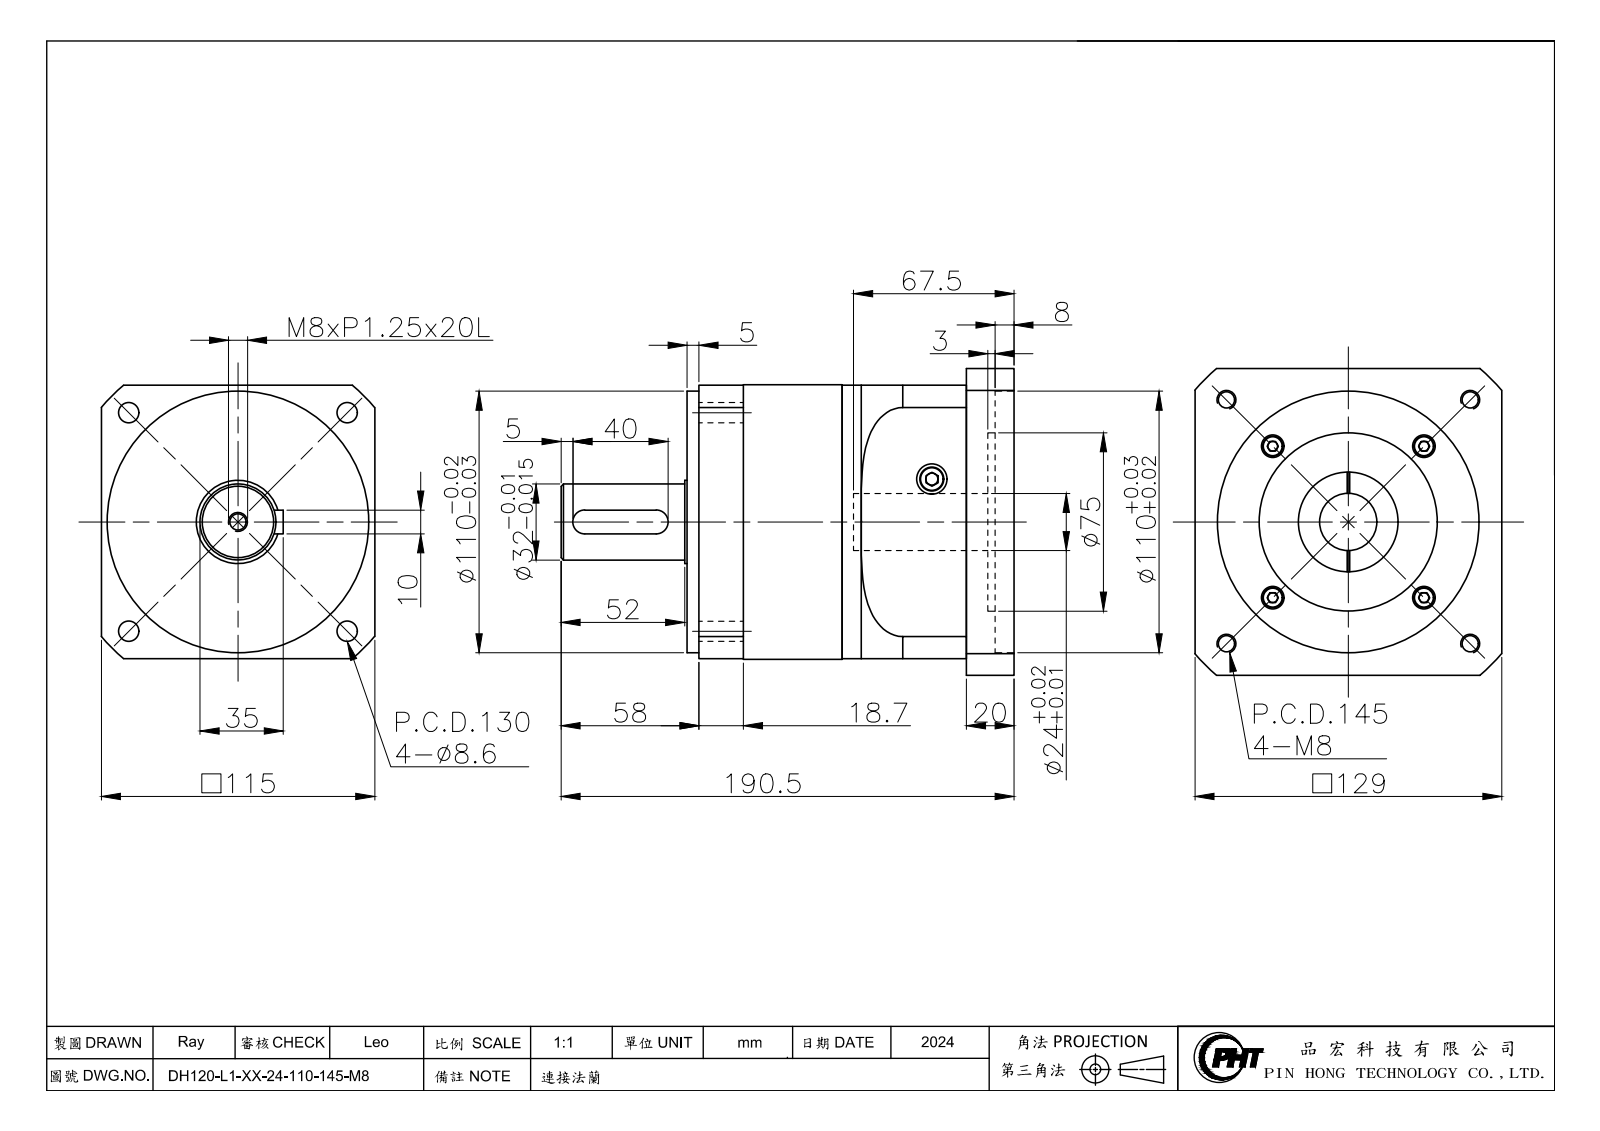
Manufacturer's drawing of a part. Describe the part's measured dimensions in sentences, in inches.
The part is named "DH120-L1-XX-24-110-145-M8(連接法蘭)_2024". Its 3-D file was written by "SolidWorks 2016 (CONFIG_CONTROL_DESIGN)". It is 5 solids with 341 faces: 154 planar, 139 cylindrical and 48 other. Overall it measures 7.5 by 5.079 by 5.079 inches. Its volume is 94.59 cubic inches and its surface area 326.6 square inches. Round holes: 8 of diameter 0.374, 5 of diameter 0.268, 4 of diameter 0.165, 4 of diameter 0.217, 4 of diameter 0.339, 4 of diameter 0.394, 2 of diameter 0.5, 1 of diameter 0.945, 1 of diameter 1.654, 1 of diameter 2.362, 1 of diameter 2.756, 1 of diameter 2.953. Round bosses or shafts: 12 of diameter 0.335, 4 of diameter 0.197, 1 of diameter 4.547, 1 of diameter 4.528, 1 of diameter 1.929, 1 of diameter 1.378, 1 of diameter 1.26. Partial cylindrical surfaces (rounded edges, fillets, slot ends): 2 of radius 0.197, 1 of radius 2.953, 1 of radius 3.346. The main face-to-face distances are 1.634, 3.693, 2.059, 4.528, 4.626, 2.567, 0.933, 0.276, 4.803, 0.787. The hole center spacings are 0.836, 1.008, 1.206, 2.126, 2.185, 2.628, 2.832, 3.007.
